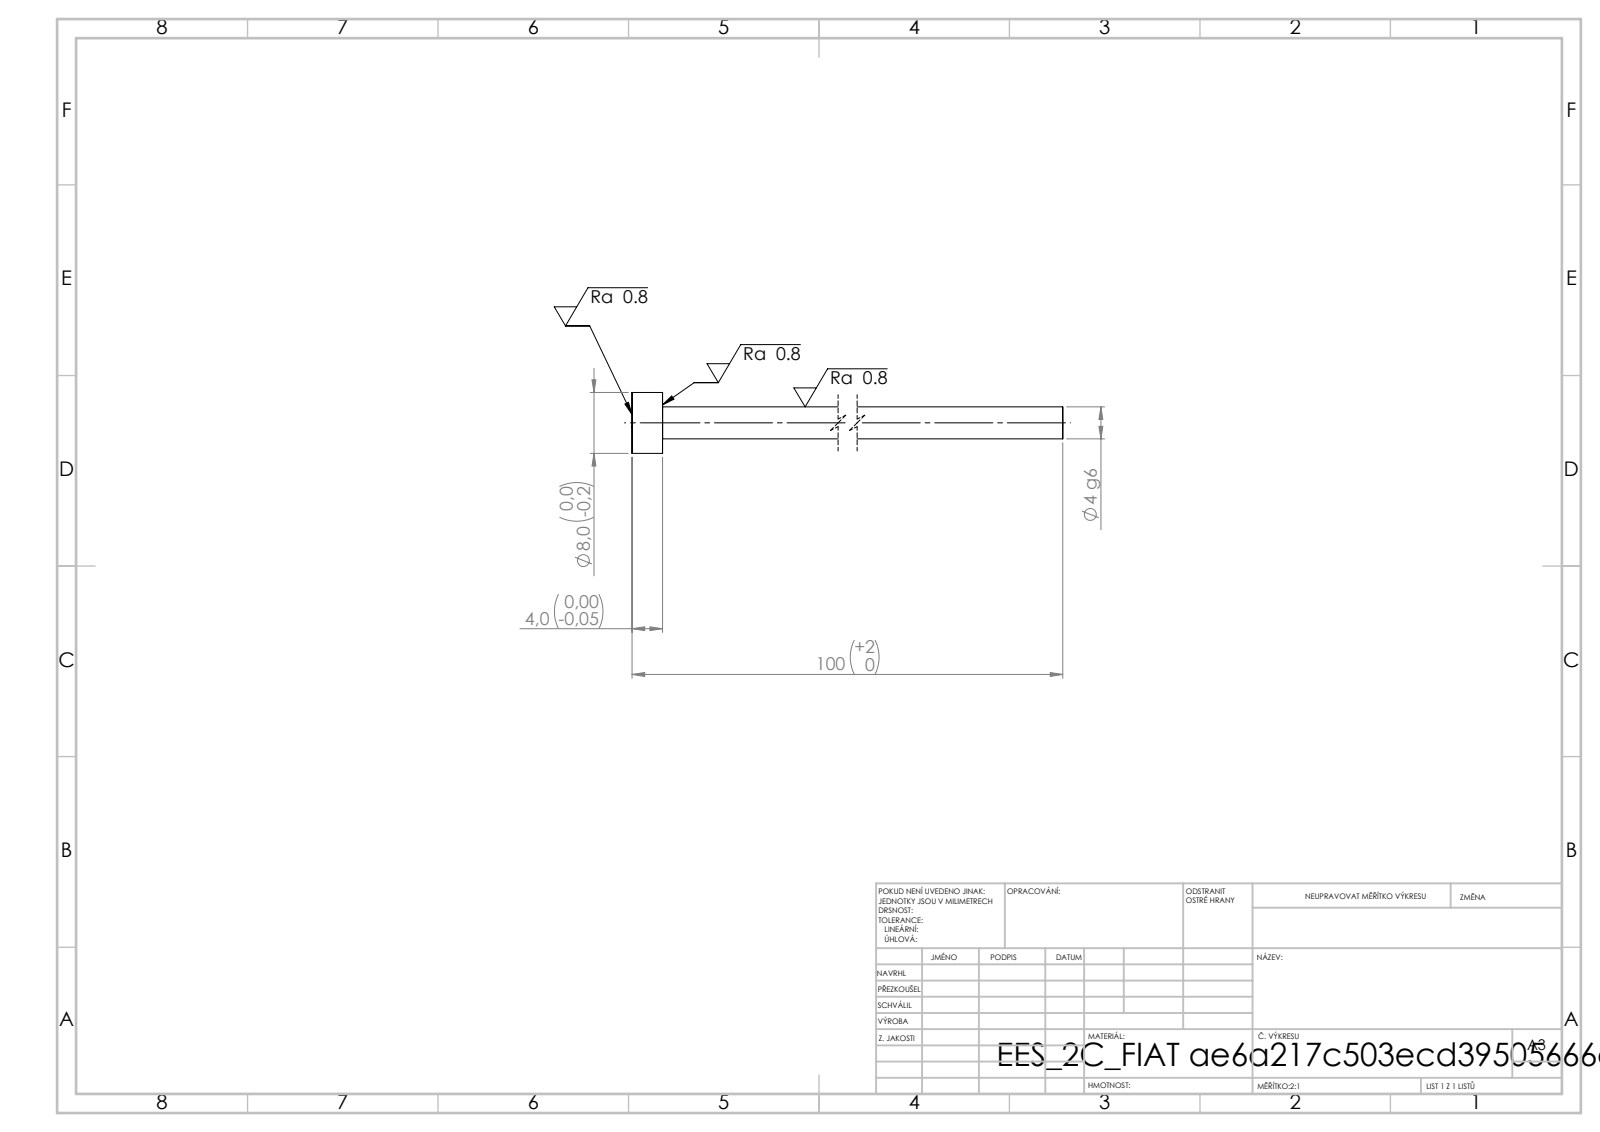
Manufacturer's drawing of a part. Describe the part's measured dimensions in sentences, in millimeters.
Its 3-D file was written by "SolidWorks 2019 (CONFIG_CONTROL_DESIGN)". It is 1 solid with 7 faces: 3 planar, 4 cylindrical and 0 other. Overall it measures 100 by 8 by 8 millimeters. Its volume is 1 531 cubic millimeters and its surface area 1 468 square millimeters. Round bosses or shafts: 1 of diameter 8, 1 of diameter 4.2. The main face-to-face distances are 4, 100, 96.
